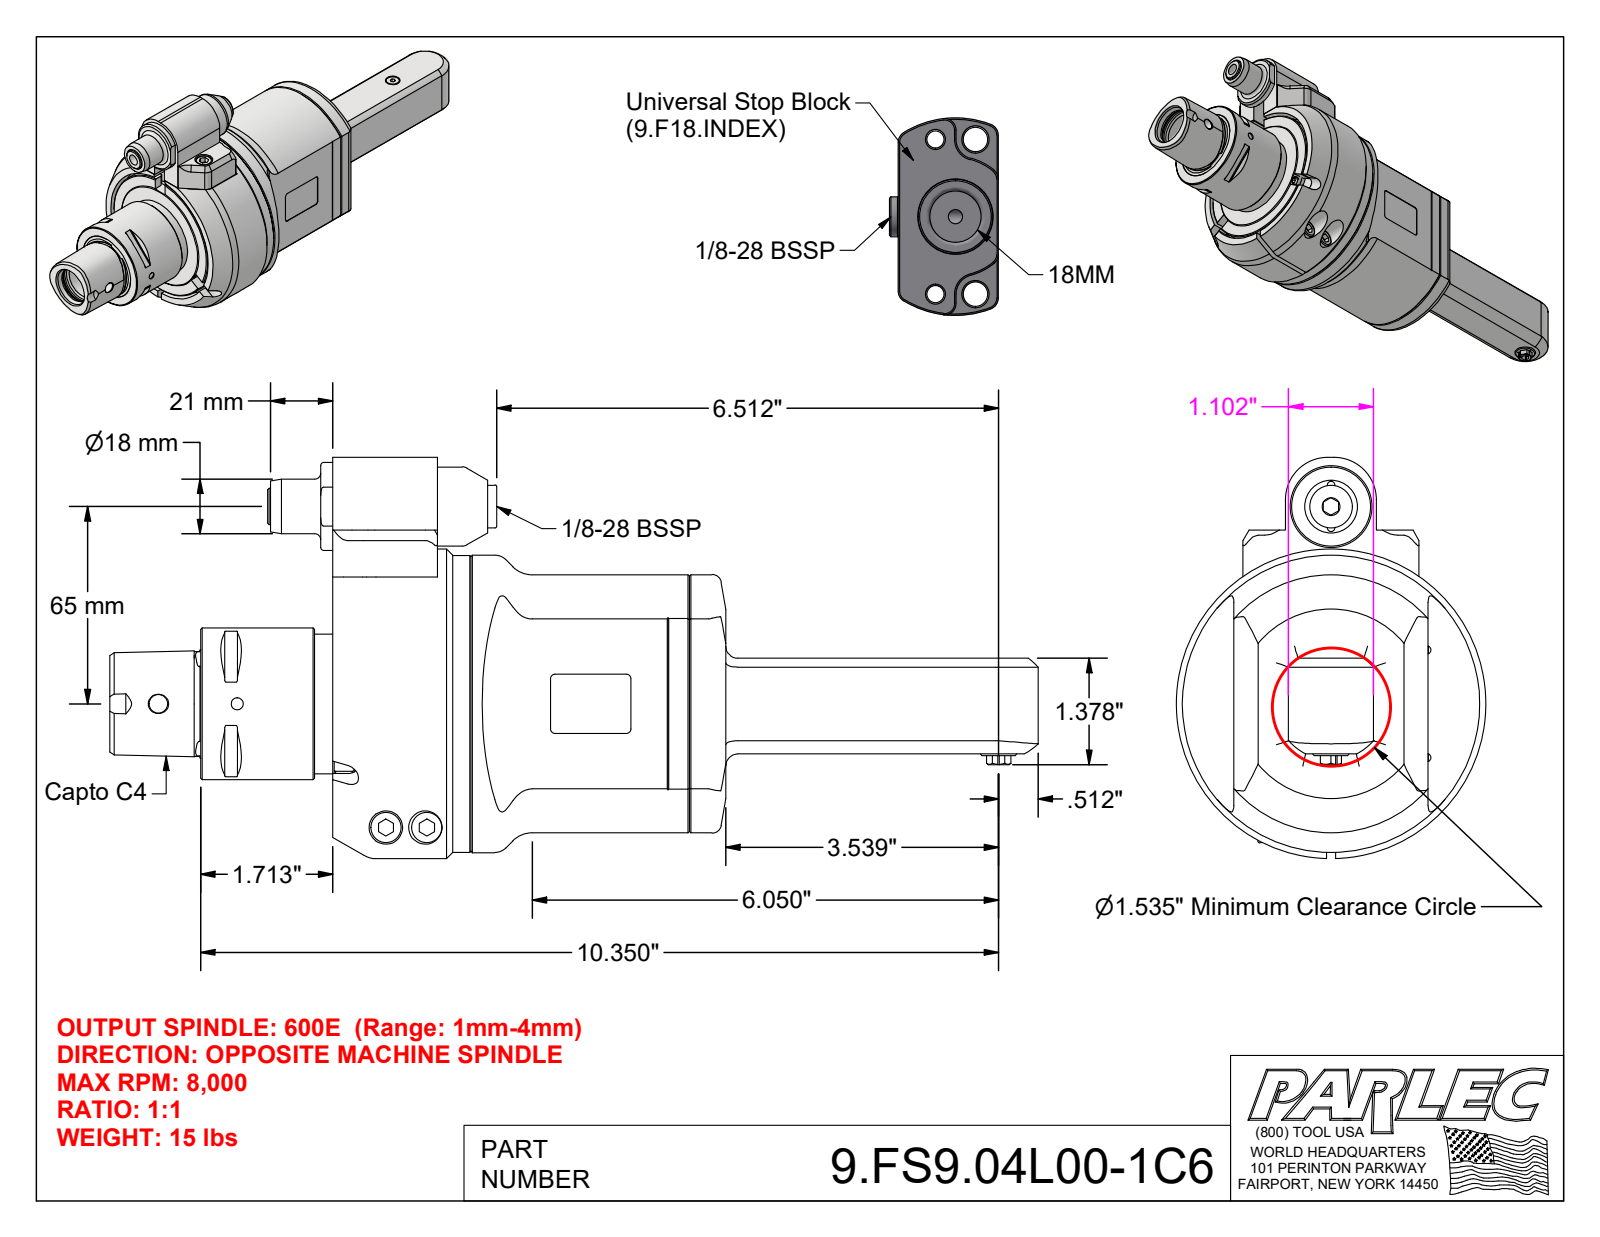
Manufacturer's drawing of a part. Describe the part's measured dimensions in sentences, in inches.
The part is named "9.FS9.04L00-1C6; 9_GA1_656_2 (Type 1, Capto C6, 65mm); 9_FS9_04L00". Its 3-D file was written by "Autodesk Inventor 2022 (AUTOMOTIVE_DESIGN)". It is 5 solids with 506 faces: 254 planar, 125 cylindrical and 127 other. Overall it measures 12.043 by 5.206 by 4.016 inches. Its volume is 60.9 cubic inches and its surface area 215.2 square inches. Round holes: 2 of diameter 0.102, 2 of diameter 0.118, 2 of diameter 0.157, 2 of diameter 0.165, 2 of diameter 0.197, 2 of diameter 0.335, 2 of diameter 0.409, 2 of diameter 0.433, 1 of diameter 0.098, 1 of diameter 0.24, 1 of diameter 0.256, 1 of diameter 0.276. Round bosses or shafts: 4 of diameter 0.394, 4 of diameter 0.236, 3 of diameter 0.315, 2 of diameter 0.098, 1 of diameter 4.016, 1 of diameter 3.858, 1 of diameter 3.85, 1 of diameter 3.031. Partial cylindrical surfaces (rounded edges, fillets, slot ends): 11 of radius 0.157, 8 of radius 0.012, 8 of radius 0.079, 4 of radius 0.059, 3 of radius 0.551, 2 of radius 0.02, 2 of radius 0.039, 2 of radius 0.138. The main face-to-face distances are 0.709, 0.118, 1.811, 1.26, 1.378, 1.555, 0.177, 0.157, 1.102, 0.02. The hole center spacings are 0.276, 0.512, 0.551, 1.024, 1.081, 1.72, 2.283, 2.508.
